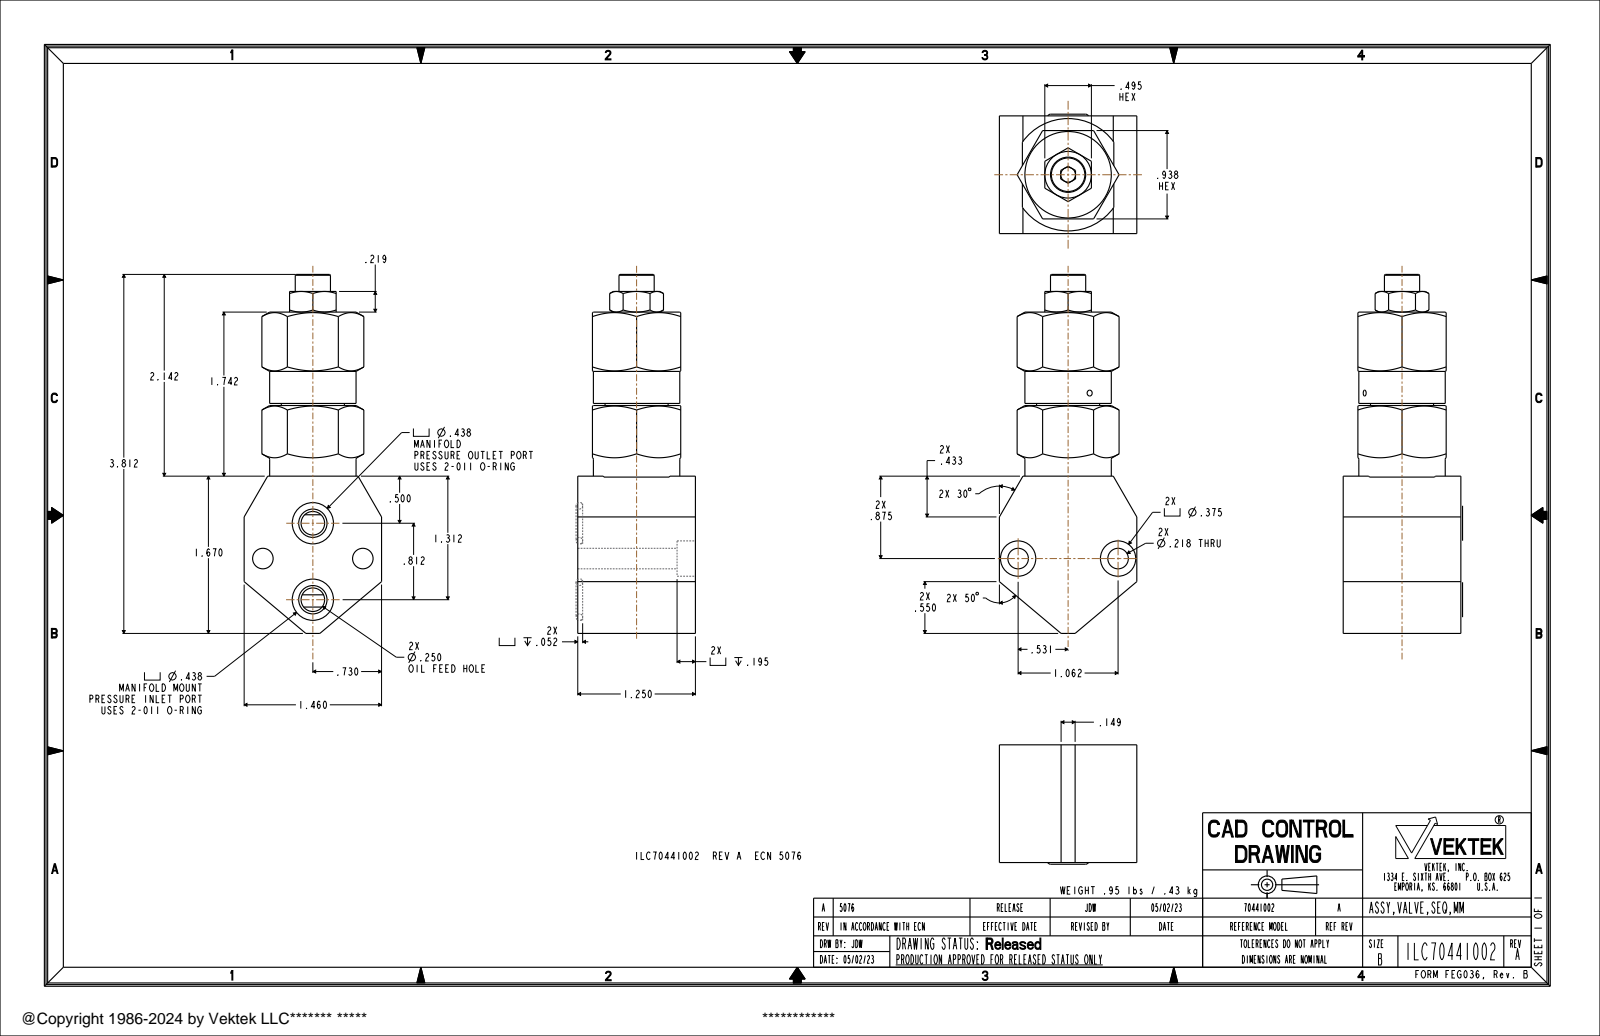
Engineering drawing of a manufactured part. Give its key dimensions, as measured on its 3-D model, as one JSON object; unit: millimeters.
{"part_name": "ILC70441002", "step_written_by": "CREO PARAMETRIC BY PTC INC, 2021164 (AUTOMOTIVE_DESIGN)", "units": "millimeters", "bodies": {"solids": 1, "faces": 148, "planar": 51, "cylindrical": 49, "other": 48}, "overall_size": [96.8, 37.1, 32.2], "volume_mm3": 44340, "surface_area_mm2": 17790, "round_holes": [[5.5, 2], [6.4, 2], [9.5, 2], [11.1, 2], [1.6, 1], [4, 1], [12.7, 1], [16, 1], [17.4, 1], [18.6, 1]], "round_bosses_or_shafts": [[23.3, 1], [17, 1], [9.5, 1]], "partial_cylinders_radius": [[15.1, 1]], "face_to_face_distances": [23.8, 31.8, 4, 27.8, 37.1, 44.5, 7.3, 37.2, 24.6, 17.3], "hole_center_spacings": [16.5, 17.5, 20.6, 27]}
